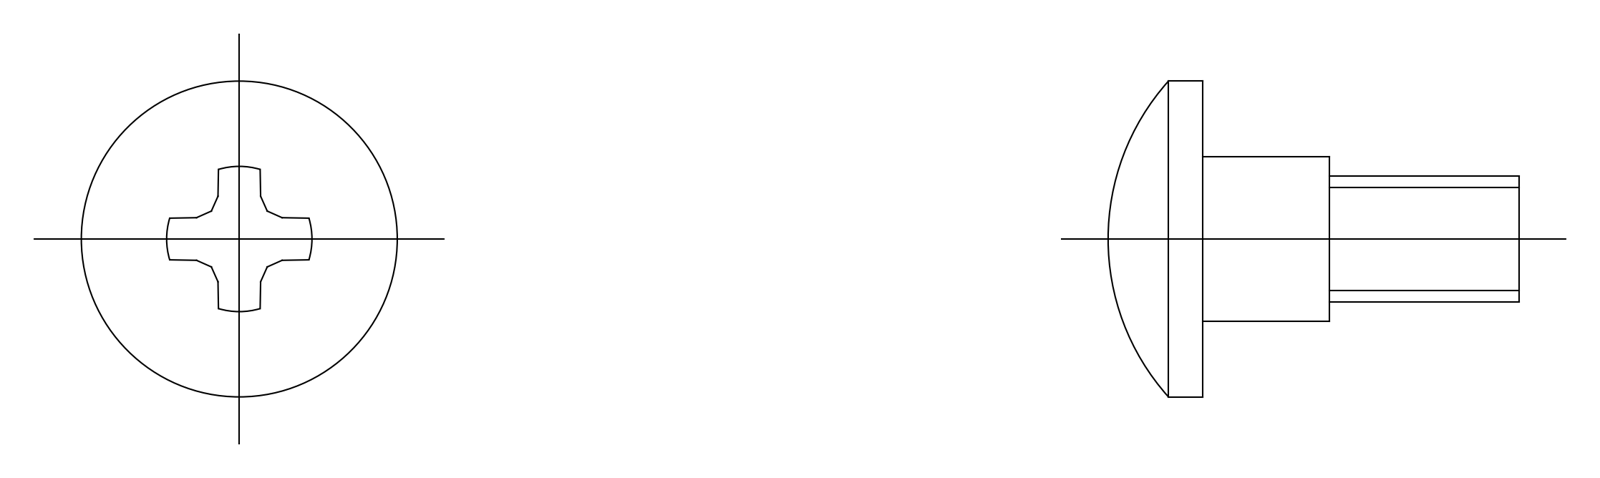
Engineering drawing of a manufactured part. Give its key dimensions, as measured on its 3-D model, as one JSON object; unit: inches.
{"step_written_by": "spGate 19.8.4 (****-****-****-****) (AUTOMOTIVE_DESIGN)", "units": "inches", "bodies": {"solids": 1, "faces": 32, "planar": 20, "cylindrical": 10, "other": 2}, "overall_size": [0.507, 0.394, 0.394], "volume_in3": 0.019, "surface_area_in2": 0.55, "round_bosses_or_shafts": [[0.394, 1], [0.205, 1], [0.157, 1]], "partial_cylinders_radius": [[0.091, 1]], "face_to_face_distances": [0.236, 0.394, 0.079, 0.472, 0.157, 0.055, 0.092]}
